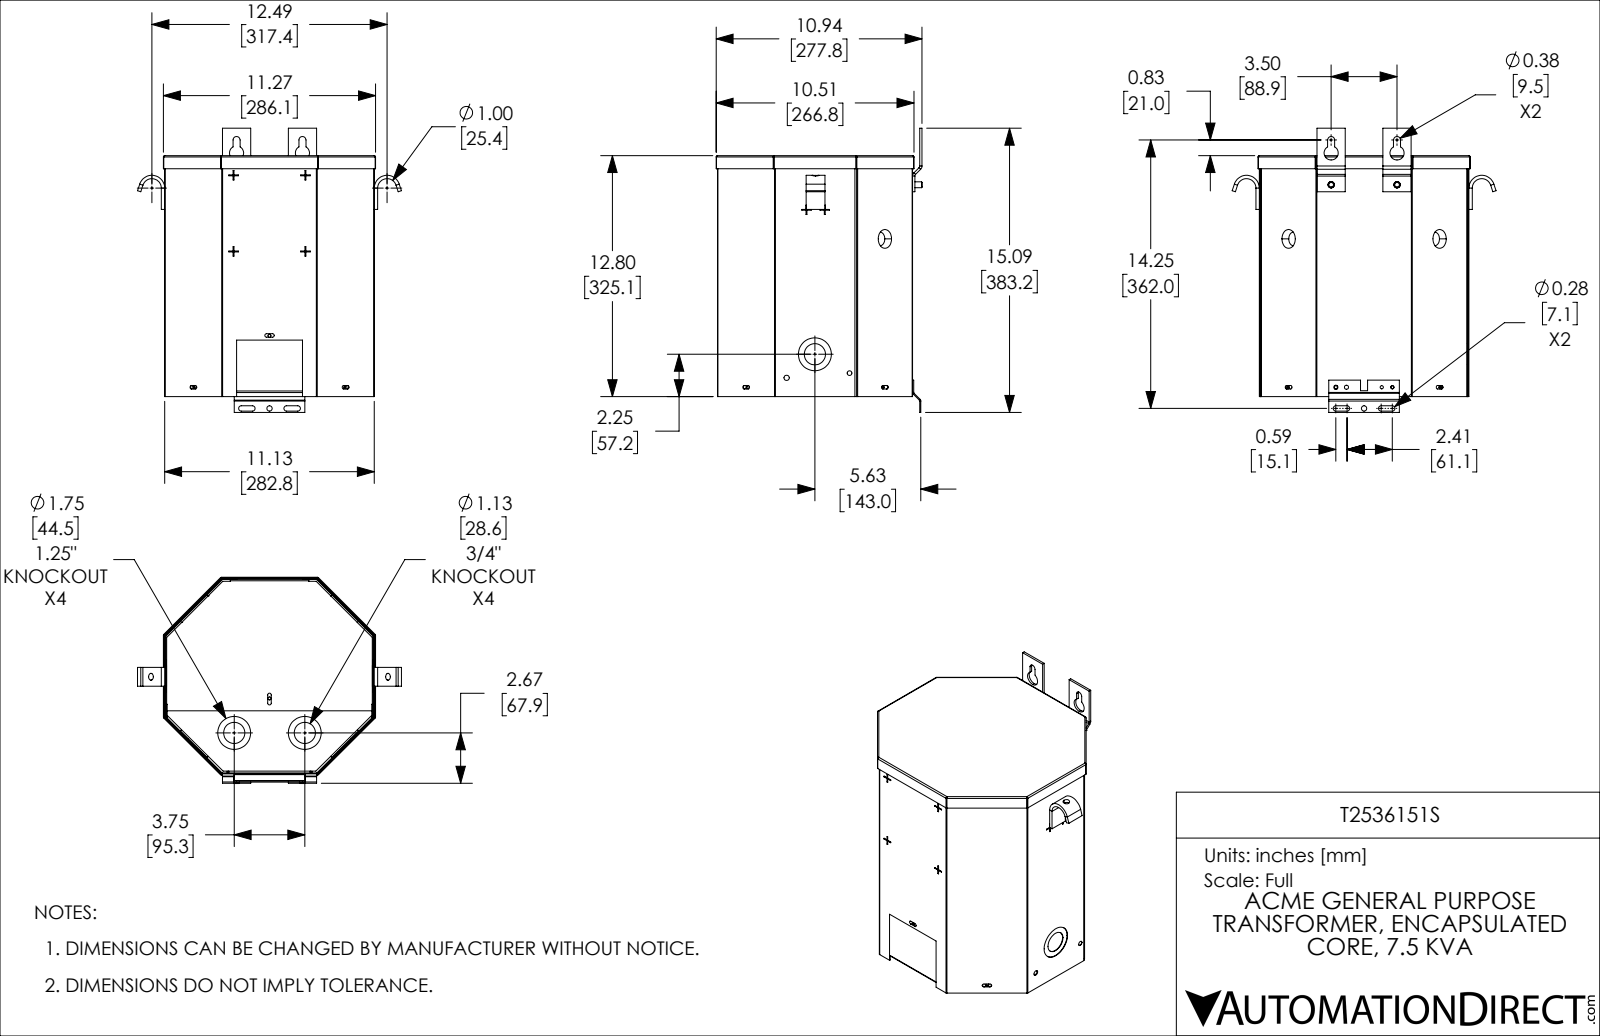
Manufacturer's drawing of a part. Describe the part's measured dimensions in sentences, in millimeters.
The part is named "T2536151S". Its 3-D file was written by "SolidWorks 2021 (CONFIG_CONTROL_DESIGN)". It is 13 solids with 643 faces: 422 planar, 185 cylindrical and 36 other. Overall it measures 383.16 by 356.02 by 278.11 millimeters. Its volume is 623 125 cubic millimeters and its surface area 974 373 square millimeters. Round holes: 5 of diameter 4.04, 3 of diameter 4.06, 3 of diameter 28.58, 3 of diameter 44.45, 2 of diameter 4.37, 2 of diameter 5.56, 2 of diameter 6.35, 2 of diameter 6.5, 2 of diameter 7.14, 2 of diameter 7.92, 2 of diameter 7.94, 2 of diameter 8.73. Round bosses or shafts: 1 of diameter 7.92. Partial cylindrical surfaces (rounded edges, fillets, slot ends): 16 of radius 0.61, 16 of radius 1.82, 14 of radius 2.38, 4 of radius 3.57, 3 of radius 0.86, 3 of radius 1.27, 3 of radius 2.06, 3 of radius 2.48. The main face-to-face distances are 1.22, 1.21, 275.79, 277, 281.6, 274.58, 1.2, 316.45, 318.21, 319.43. The hole center spacings are 88.9, 282.58, 14.29, 61.91, 273.12, 285.26, 0.8, 42.86.
